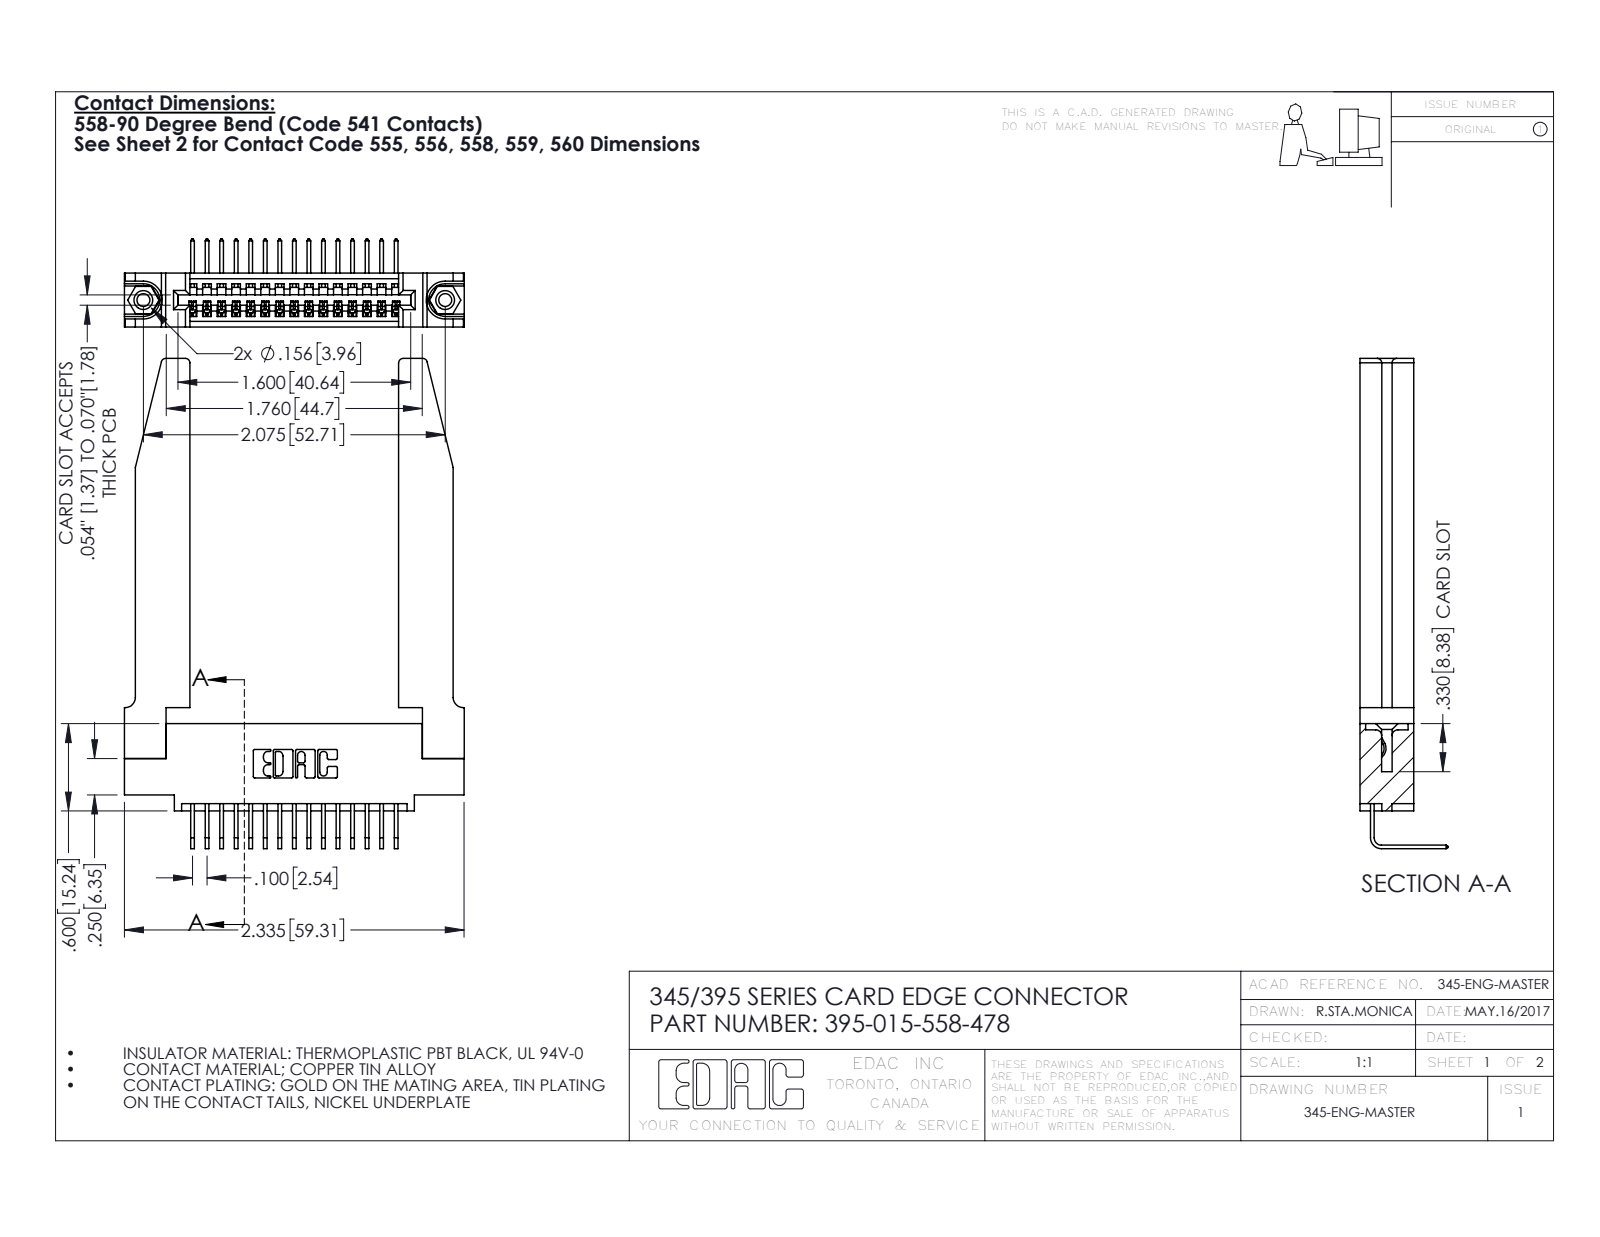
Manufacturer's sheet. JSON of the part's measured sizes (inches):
{"part_name": "345 Part_0.110 Offset - 0.156 Dia-TH; 345-292-001_558 Tail - 2; 345-220-078_345-220-078; 345-250-001_345-250-001-102 (+1 more)", "step_written_by": "SolidWorks 2016 (CONFIG_CONTROL_DESIGN)", "units": "inches", "bodies": {"solids": 20, "faces": 1264, "planar": 856, "cylindrical": 356, "other": 52}, "overall_size": [3.369, 2.336, 0.605], "volume_in3": 0.803, "surface_area_in2": 21.73, "round_holes": [[0.089, 2], [0.125, 2], [0.156, 2], [0.064, 1]], "round_bosses_or_shafts": [[0.155, 2]], "partial_cylinders_radius": [[0.006, 30], [0.01, 22], [0.03, 8], [0.007, 6], [0.031, 6], [0.026, 3], [0.031, 2], [0.04, 2]], "face_to_face_distances": [0.37, 0.072, 0.298, 0.15, 0.148, 0.22, 0.077, 0.2, 0.098, 0.272], "hole_center_spacings": [0.27, 1.842, 2.075]}
